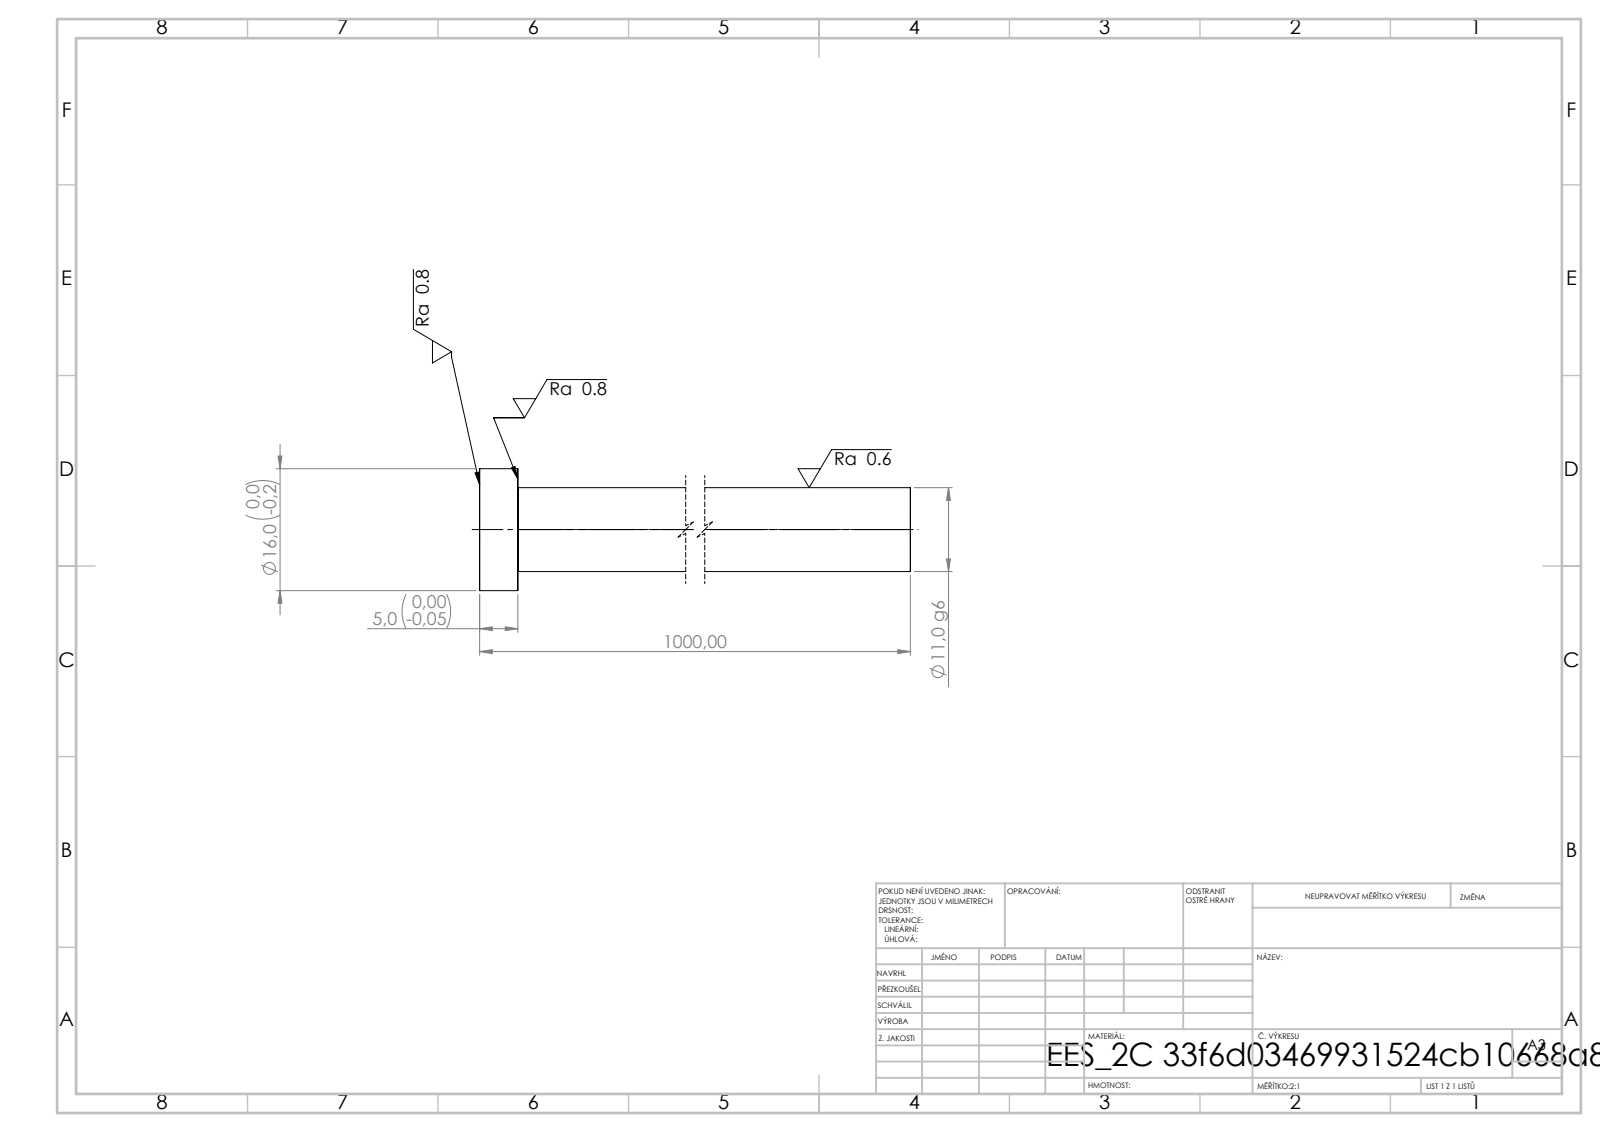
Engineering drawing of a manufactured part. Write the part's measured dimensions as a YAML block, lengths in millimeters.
step_written_by: "SolidWorks 2019 (CONFIG_CONTROL_DESIGN)"
units: millimeters
bodies: {solids: 1, faces: 7, planar: 3, cylindrical: 4, other: 0}
overall_size: [1000, 16, 16]
volume: 95563
surface_area: 35038
round_bosses_or_shafts:
  - {diameter: 16, count: 1}
  - {diameter: 11, count: 1}
face_to_face_distances: [5, 1000, 995]
